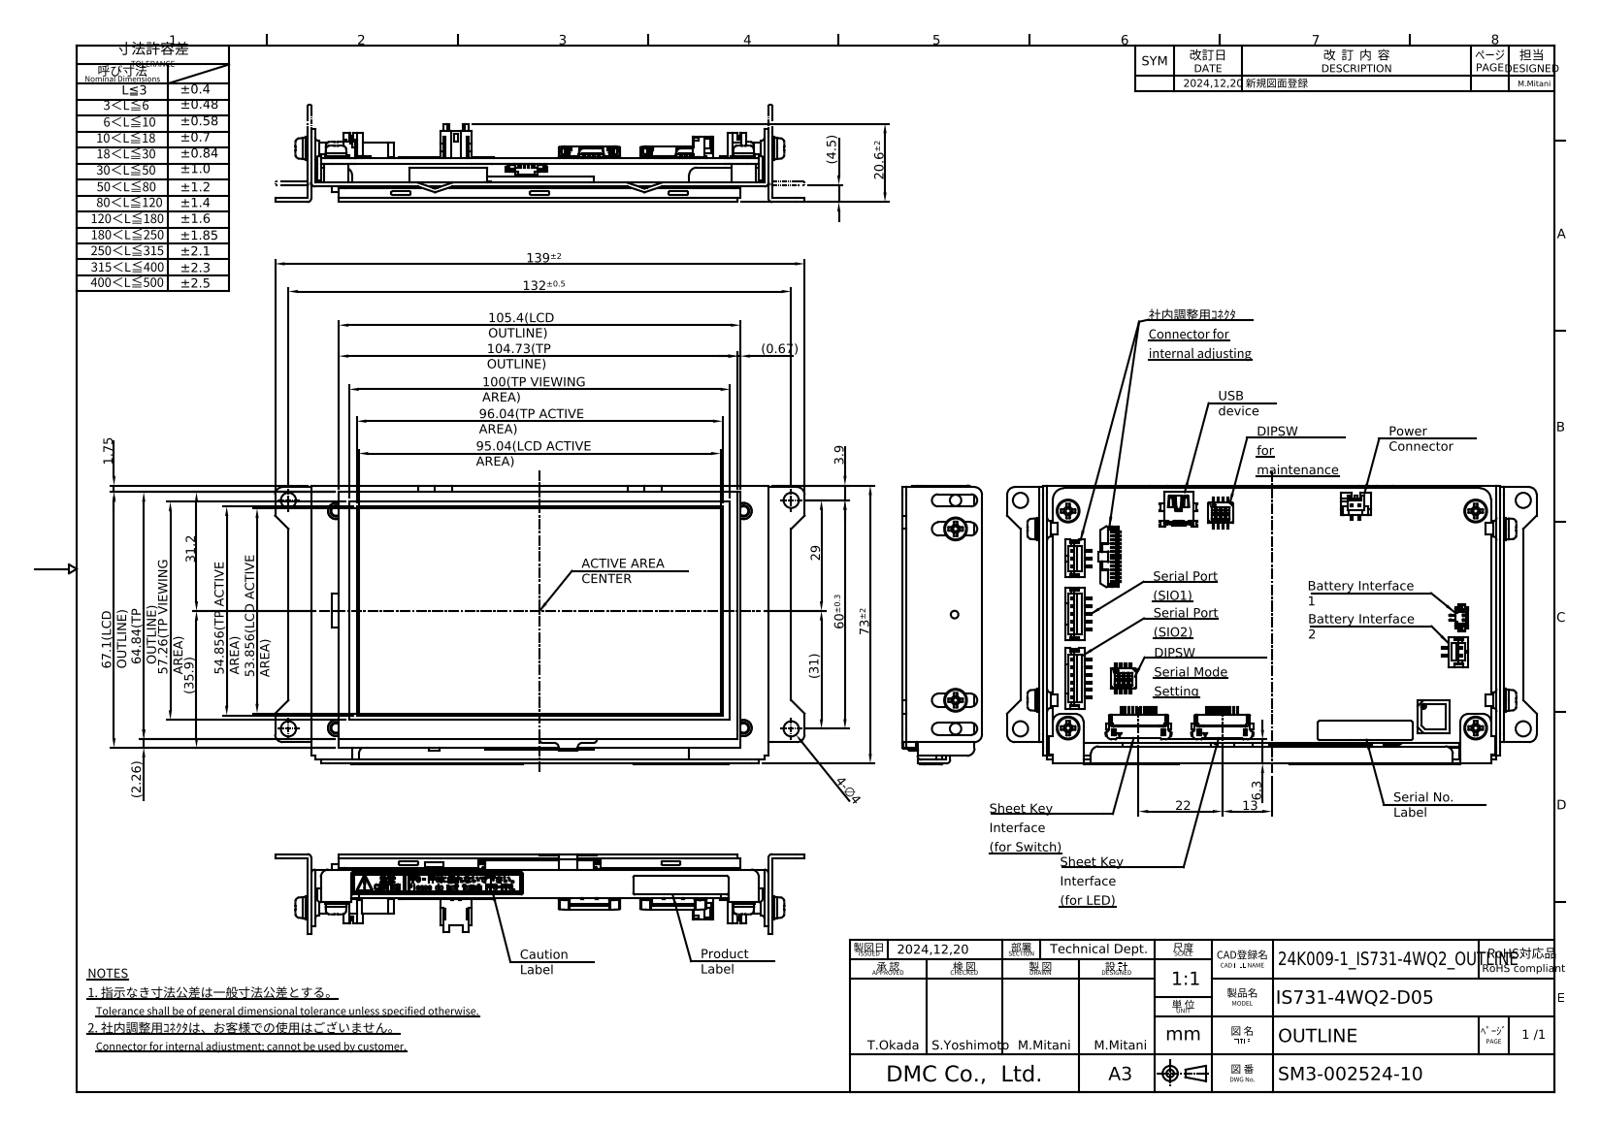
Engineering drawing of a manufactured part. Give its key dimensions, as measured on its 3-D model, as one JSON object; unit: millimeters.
{"part_name": "HP_IS731-4WQ2-D05", "step_written_by": "Autodesk Inventor 2020 (AUTOMOTIVE_DESIGN)", "units": "millimeters", "bodies": {"solids": 1, "faces": 7300, "planar": 5503, "cylindrical": 1158, "other": 639}, "overall_size": [139, 73.2, 21], "volume_mm3": 58293, "surface_area_mm2": 98937, "round_holes": [[4, 6], [2.46, 4], [3.5, 4], [4.25, 4], [1.2, 2], [0.3, 1], [1.33, 1], [2, 1]], "round_bosses_or_shafts": [[3, 8], [6, 6], [5.5, 6], [8, 4], [6.5, 4], [4.24, 4]], "partial_cylinders_radius": [[0.1, 177], [0.3, 91], [0.2, 82], [0.15, 63], [0.5, 24], [0.25, 23], [2, 20], [1, 17]], "face_to_face_distances": [1, 1.6, 1.55, 9.01, 1.25, 1.3, 4.06, 6.6, 7.6, 11.66], "hole_center_spacings": [12.5, 12.81, 57, 58.55, 60, 61.09, 107, 119.5]}
